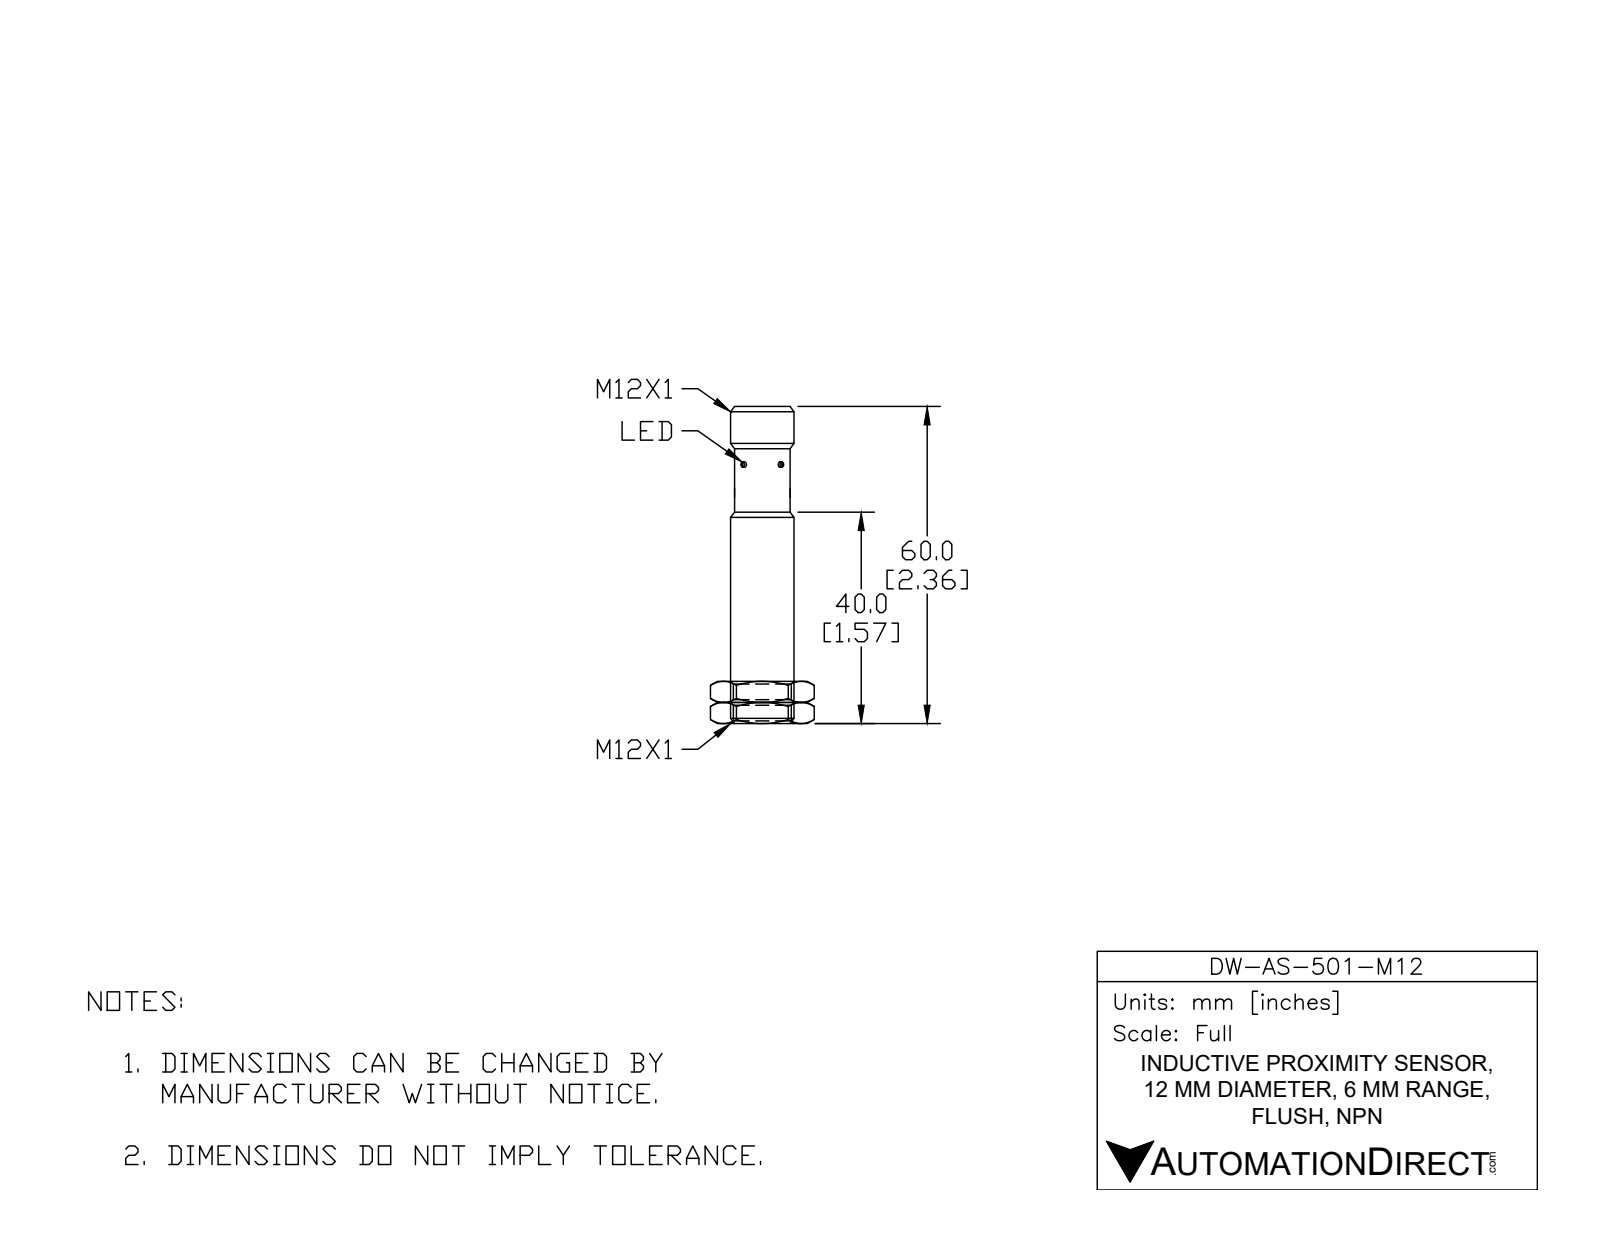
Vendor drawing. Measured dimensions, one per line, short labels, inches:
name: DW-AS-501-M12
written by: SolidWorks 2017 (AUTOMOTIVE_DESIGN)
unit: in
bodies: 1 solid, 35 faces (7 planar, 19 cylindrical, 9 other)
size: 2.362 × 0.472 × 0.472
volume: 0.367 in³; area: 4.348 in²
holes: 2× ⌀0.118, 1× ⌀0.335
bosses: 4× ⌀0.039, 1× ⌀0.472, 1× ⌀0.415
rounds: 2× R0.022, 1× R0.193
face distances: 2.02, 2.362, 0.343, 0.043, 1.614, 0.406, 0.748, 2.047, 0.433, 0.028
